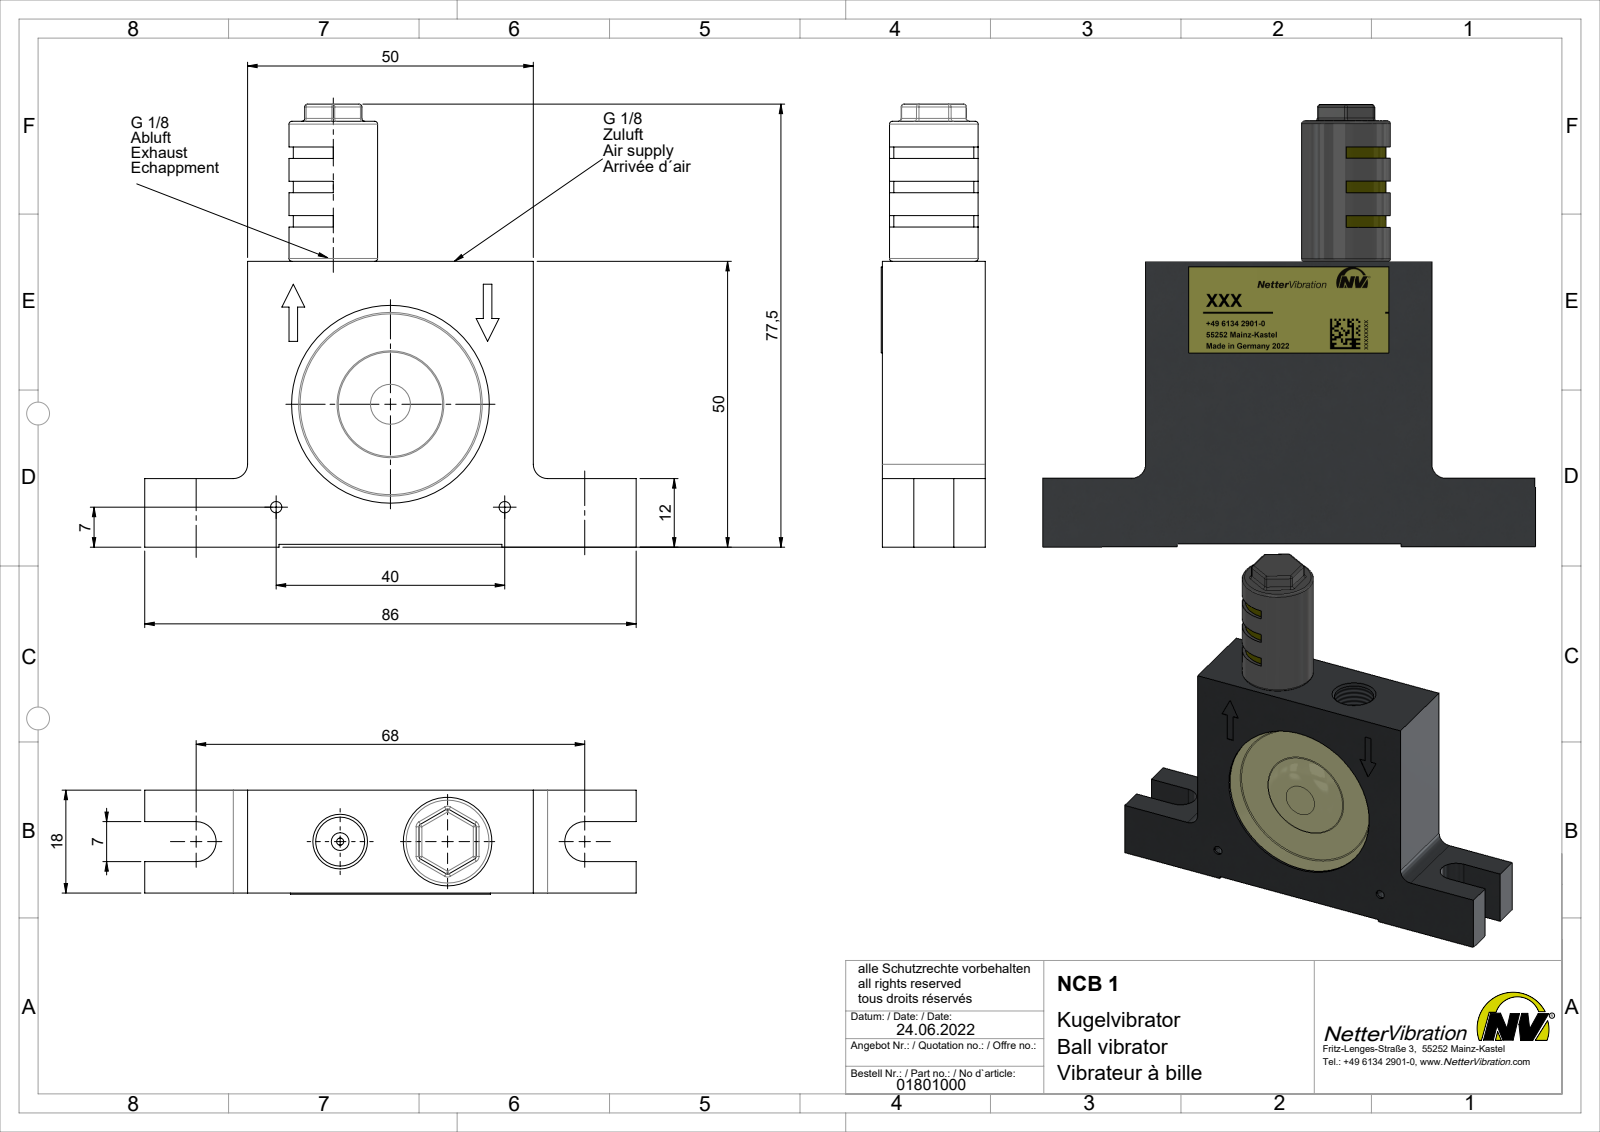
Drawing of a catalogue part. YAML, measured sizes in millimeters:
part_name: "NCB 1 Kugelvibrator #01801000"
step_written_by: "SolidWorks 2015 (AUTOMOTIVE_DESIGN)"
units: millimeters
bodies: {solids: 3, faces: 222, planar: 102, cylindrical: 49, other: 71}
overall_size: [86, 77.5, 18]
volume: 50483
surface_area: 15959
round_holes:
  - {diameter: 2, count: 2}
  - {diameter: 8.57, count: 2}
  - {diameter: 1.25, count: 1}
  - {diameter: 6, count: 1}
  - {diameter: 33, count: 1}
  - {diameter: 34.6, count: 1}
round_bosses_or_shafts:
  - {diameter: 15.5, count: 1}
  - {diameter: 9.73, count: 1}
partial_cylinders:
  - {radius: 0.5, count: 18}
  - {radius: 2.5, count: 2}
  - {radius: 3.5, count: 2}
  - {radius: 7, count: 1}
face_to_face_distances: [18, 50, 0.5, 5, 13, 49.5, 12, 5.5, 12.5, 38]
hole_center_spacings: [26.91, 18.8, 40]
